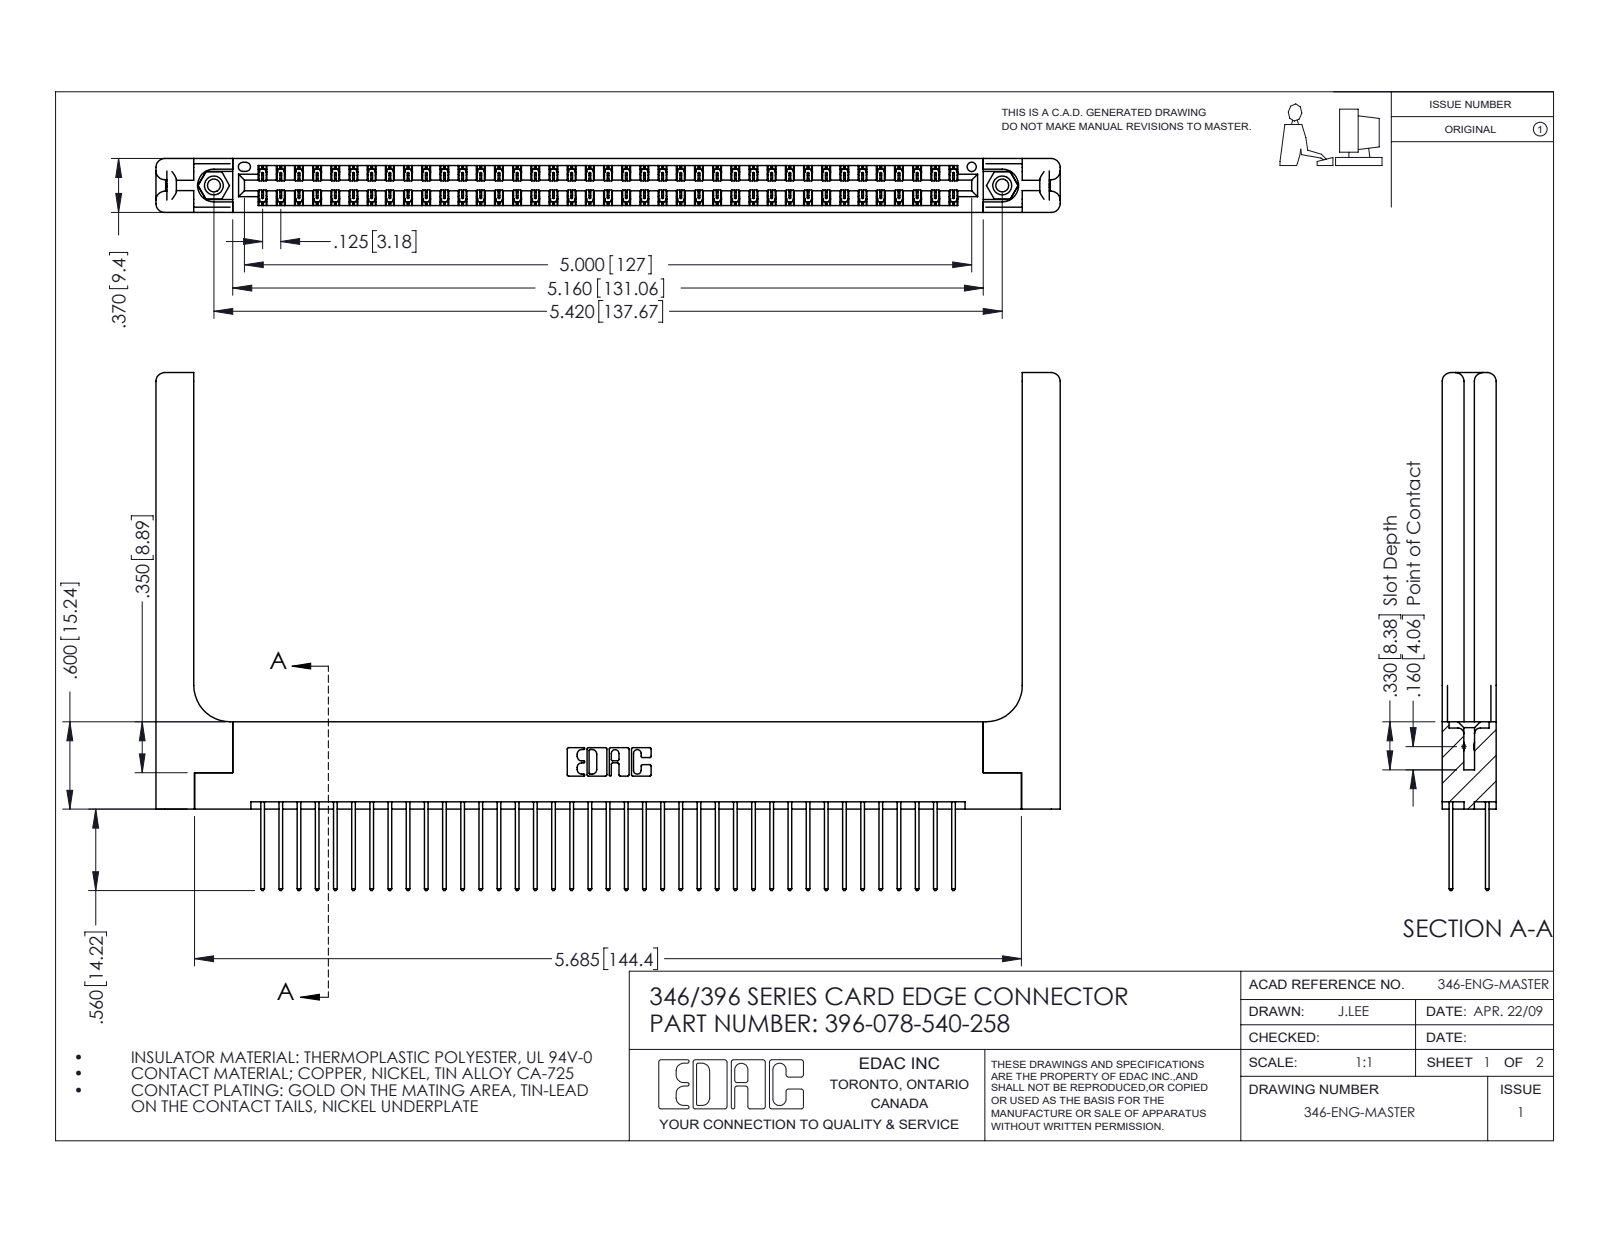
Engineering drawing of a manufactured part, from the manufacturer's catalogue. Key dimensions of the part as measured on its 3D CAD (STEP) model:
Part name (STEP PRODUCT): 345-292-001_345-293-140; 345-250-001_345-250-001-102; 346 Part_Flush Mounting Lugs - 0.156 Dia-TH; 396-078-540-258 (+1 more)
STEP written by: SolidWorks 2016 (CONFIG_CONTROL_DESIGN)
Units: inches
Bodies: 83 solids, 4434 faces (2954 planar, 1420 cylindrical, 60 other)
Overall size (bounding box): 6.216 × 3.56 × 0.37
Volume: 1.413 in³ · Surface area: 43.19 in²
Round holes (diameter × count): ⌀0.089 ×2, ⌀0.125 ×2, ⌀0.156 ×2, ⌀0.064 ×1
Round bosses / shafts (diameter × count): ⌀0.155 ×2
Partial cylindrical surfaces — rounded edges, fillets, slot ends (radius × count): R0.006 ×117, R0.01 ×78, R0.01 ×22, R0.06 ×16, R0.007 ×6, R0.031 ×6, R0.026 ×3, R0.014 ×2
Main face-to-face distances: 0.048, 0.322, 0.072, 0.37, 0.25, 0.025, 0.298, 0.148, 0.15, 0.275
Hole centre spacings: 0.246, 5.211, 5.42
